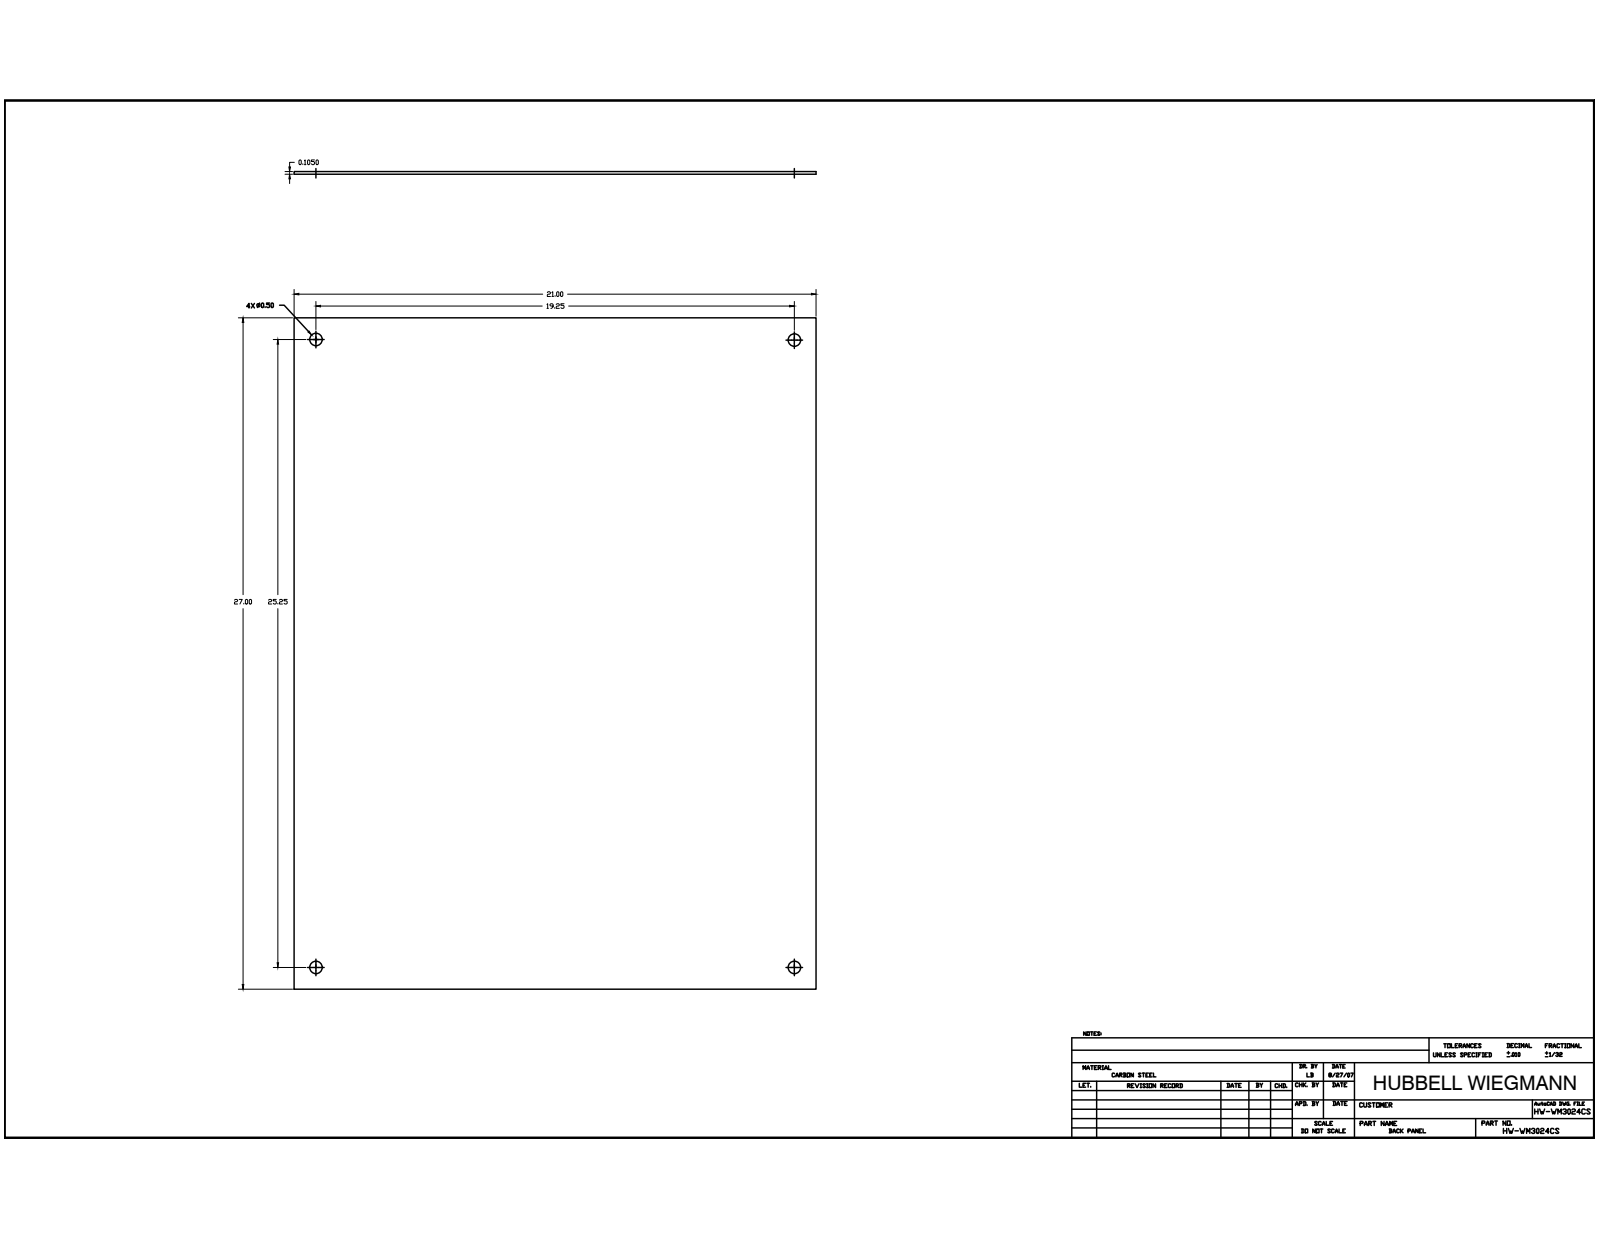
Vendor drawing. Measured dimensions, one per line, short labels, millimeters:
name: BP3024CS_STP
written by: Autodesk Inventor 2014 (AUTOMOTIVE_DESIGN)
unit: mm
bodies: 1 solid, 10 faces (6 planar, 4 cylindrical, 0 other)
size: 685.8 × 533.4 × 2.67
volume: 974 252 mm³; area: 737 527 mm²
holes: 4× ⌀12.7
face distances: 2.66, 533.4, 685.8
hole spacings: 488.94, 641.34, 806.46
